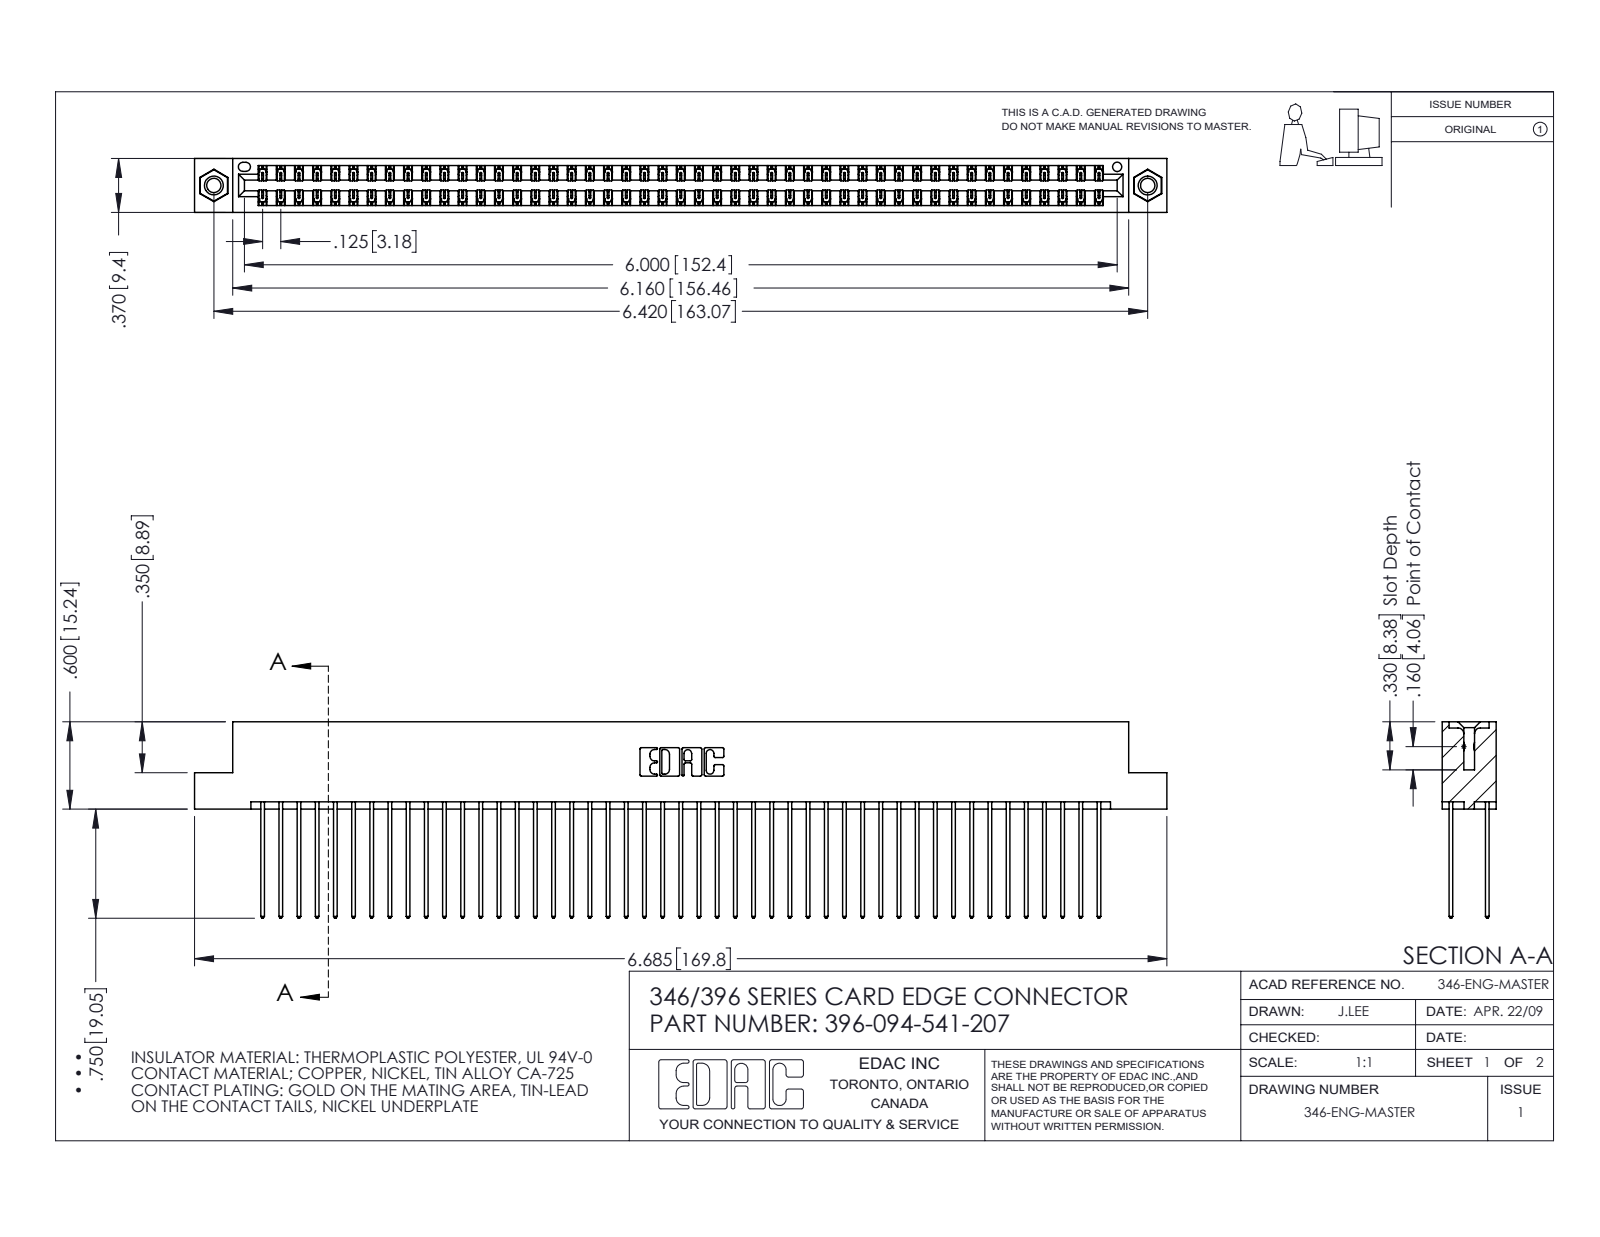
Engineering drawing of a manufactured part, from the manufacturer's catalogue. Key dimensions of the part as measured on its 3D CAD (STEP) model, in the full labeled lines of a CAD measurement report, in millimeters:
Part name (STEP PRODUCT): 396-094-541-207; 346 Part_Flush Mounting Lugs - 0.156 Dia-TI; 345-292-001_345-293-141; 345-250-001_345-250-005-103
STEP written by: SolidWorks 2016 (CONFIG_CONTROL_DESIGN)
Units: millimetres
Bodies: 97 solids, 5070 faces (3398 planar, 1656 cylindrical, 16 other)
Overall size (bounding box): 169.8 × 34.3 × 9.4
Volume: 17 120 mm³ · Surface area: 26 230 mm²
Round holes (diameter × count): ⌀2.5 ×2, ⌀3.2 ×2, ⌀4 ×2, ⌀1.6 ×1
Round bosses / shafts (diameter × count): ⌀3.9 ×2
Partial cylindrical surfaces — rounded edges, fillets, slot ends (radius × count): R0.2 ×141, R0.3 ×94, R0.3 ×22, R0.2 ×6, R0.8 ×6, R0.7 ×3, R0.4 ×2, R0.6 ×2
Main face-to-face distances: 1.2, 8.2, 6.4, 1.8, 7.6, 0.6, 9.4, 7, 5.7, 3.8
Hole centre spacings: 6.2, 157.8, 163.1
